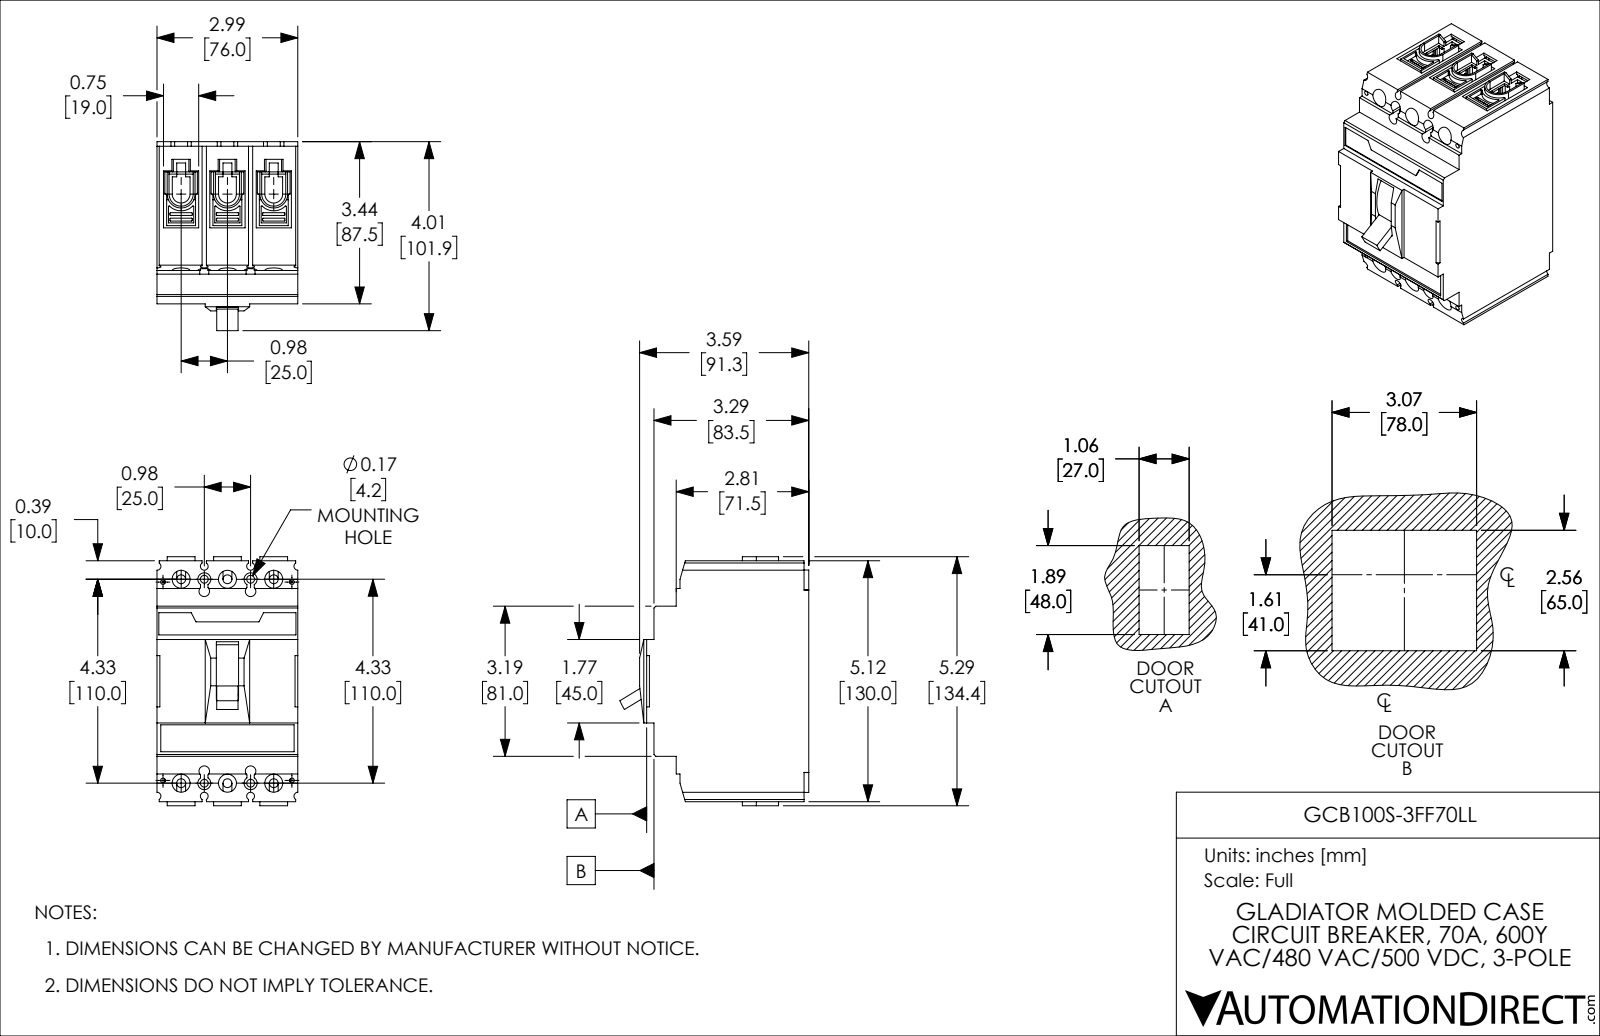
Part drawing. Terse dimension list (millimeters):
name: GCB100S-3FF70LL
written by: SolidWorks 2021 (CONFIG_CONTROL_DESIGN)
unit: mm
bodies: 1 solid, 1256 faces (784 planar, 424 cylindrical, 48 other)
size: 134.4 × 101.9 × 76
volume: 708 400 mm³; area: 95 810 mm²
holes: 8× ⌀4.2, 6× ⌀4.8, 6× ⌀9.7, 4× ⌀2.5, 4× ⌀7
rounds: 86× R0.3, 38× R0.5, 14× R1, 14× R4, 6× R0.6, 4× R2.1, 4× R2.8, 3× R4.8
face distances: 76, 25, 15.8, 114.2, 44, 2.8, 87.5, 19, 50, 130
hole spacings: 12.5, 14.3, 25, 110.7, 117.7, 112.8, 110, 7
